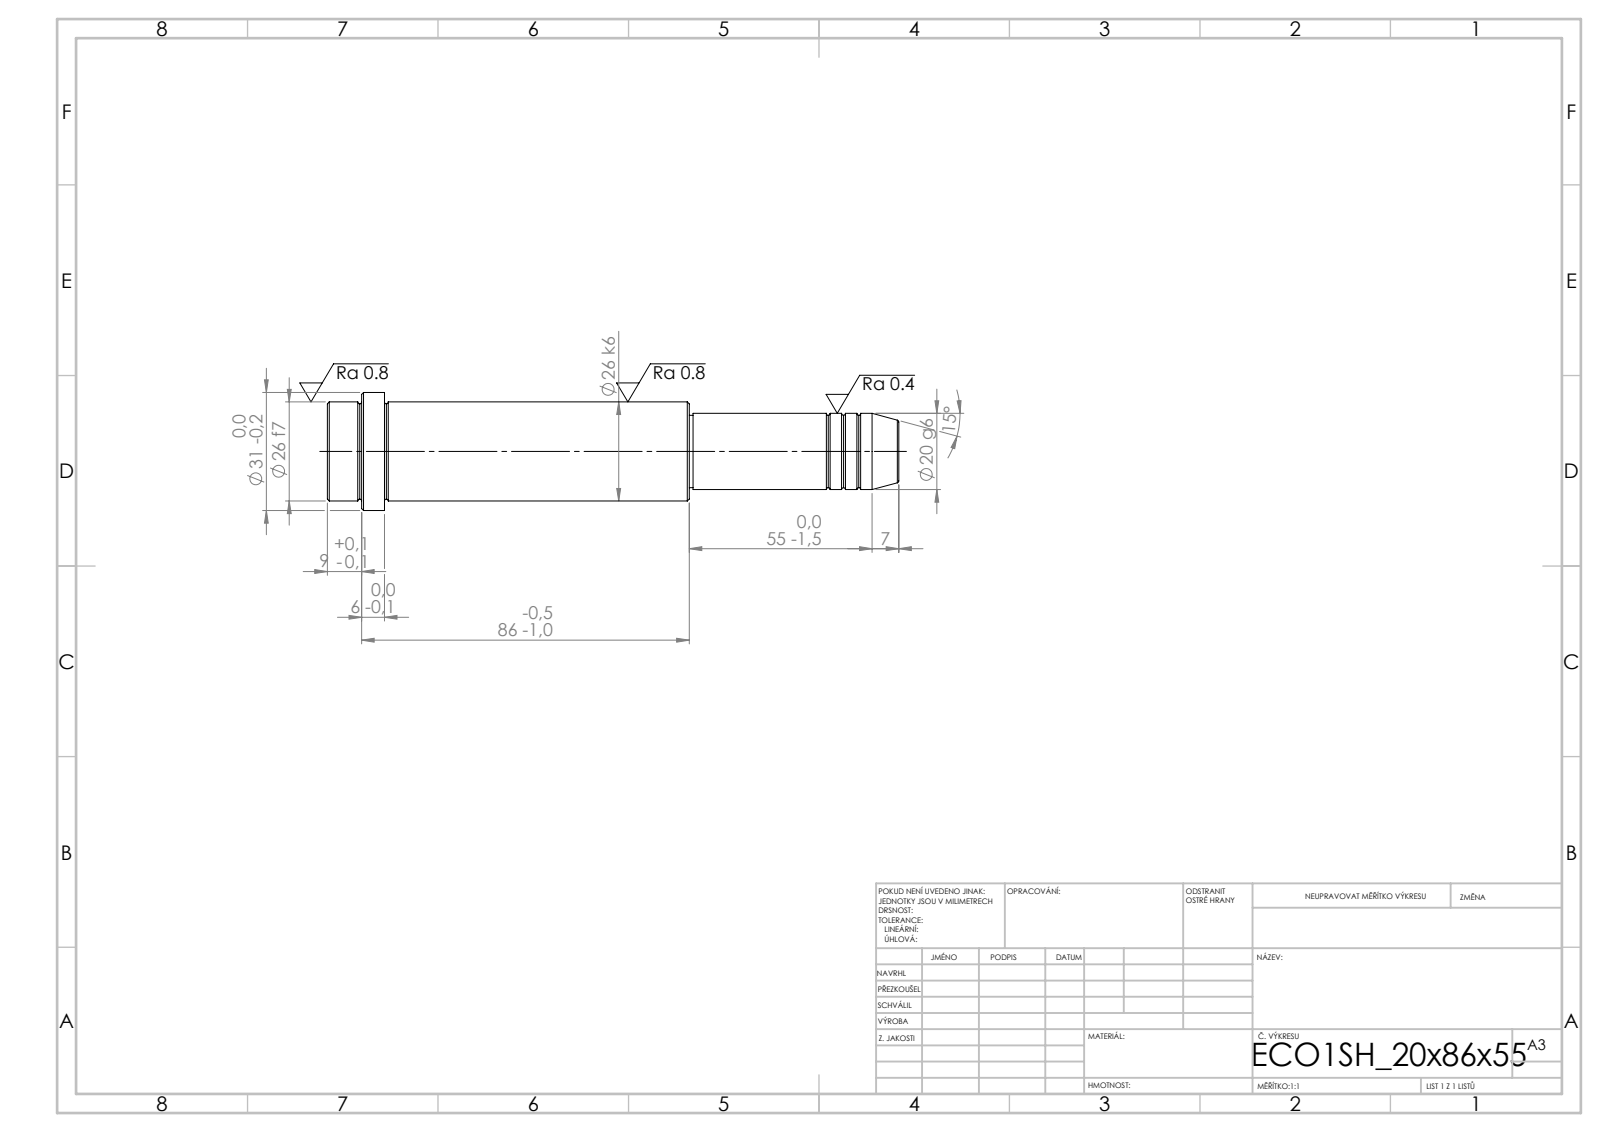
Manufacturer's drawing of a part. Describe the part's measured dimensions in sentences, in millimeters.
Its 3-D file was written by "SolidWorks 2019 (CONFIG_CONTROL_DESIGN)". It is 1 solid with 52 faces: 6 planar, 16 cylindrical and 30 other. Overall it measures 150 by 31 by 31 millimeters. Its volume is 68 474 cubic millimeters and its surface area 12 845 square millimeters. Round bosses or shafts: 1 of diameter 31, 1 of diameter 26, 1 of diameter 20, 1 of diameter 19. The main face-to-face distances are 15, 80, 95, 55, 135, 150, 141, 86, 6, 9.
